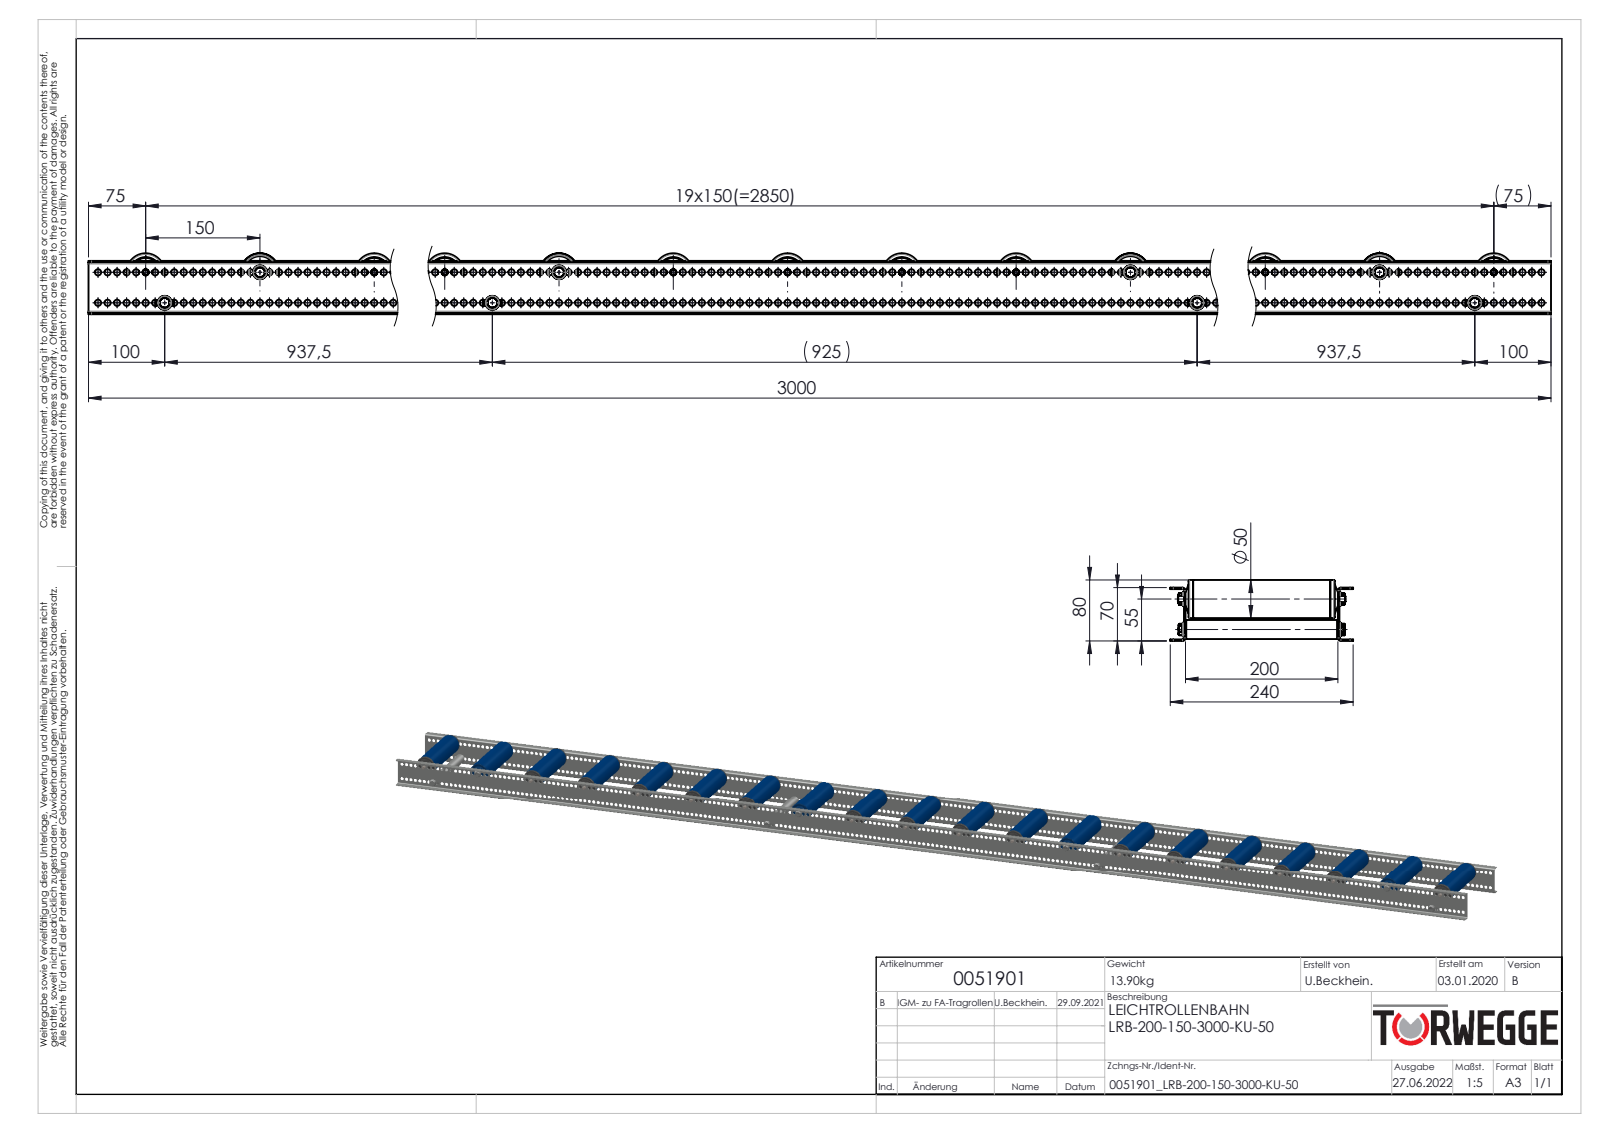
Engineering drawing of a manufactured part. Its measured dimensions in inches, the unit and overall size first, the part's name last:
Units: inches
Overall size (bounding box): 118.11 × 9.449 × 3.15
Round holes (diameter × count): ⌀0.323 ×478, ⌀0.299 ×16, ⌀0.315 ×16, ⌀0.984 ×16, ⌀1.181 ×16, ⌀1.378 ×16, ⌀1.551 ×16, ⌀1.575 ×16, ⌀0.268 ×8, ⌀0.472 ×4, ⌀0.476 ×4, ⌀0.63 ×4
Round bosses / shafts (diameter × count): ⌀1.969 ×20, ⌀1.748 ×16, ⌀1.496 ×16, ⌀1.417 ×16, ⌀1.299 ×16, ⌀0.866 ×16, ⌀0.827 ×16, ⌀0.984 ×8
Partial cylindrical surfaces — rounded edges, fillets, slot ends (radius × count): R0.024 ×32, R0.03 ×32, R0.096 ×32, R0.192 ×16, R0.276 ×16, R0.157 ×8, R0.079 ×4
Main face-to-face distances: 0.079, 7.953, 2.677, 7.874, 8.031, 2.756, 2.598, 0.236, 7.559, 0.472
Hole centre spacings: 0.492, 0.984, 1.476, 1.969, 2.461, 2.953, 3.445, 3.937
Volume: 252.1 in³ · Surface area: 5 253 in²
Bodies: 414 solids, 8412 faces (1948 planar, 3936 cylindrical, 2528 other)
Part name (STEP PRODUCT): 0039780-Achse-ST-Ø12-KFG_IGM8-AL=200; 0026266_Typ-KUT100-50x2,8-12; 0026267_Typ-KUT100-50x2,8-8_Lageboden-schematisch; 0039778-Achse-ST-Ø08-KFG_AL220-G (+8 more)
STEP written by: SolidWorks 2020 (AUTOMOTIVE_DESIGN)
